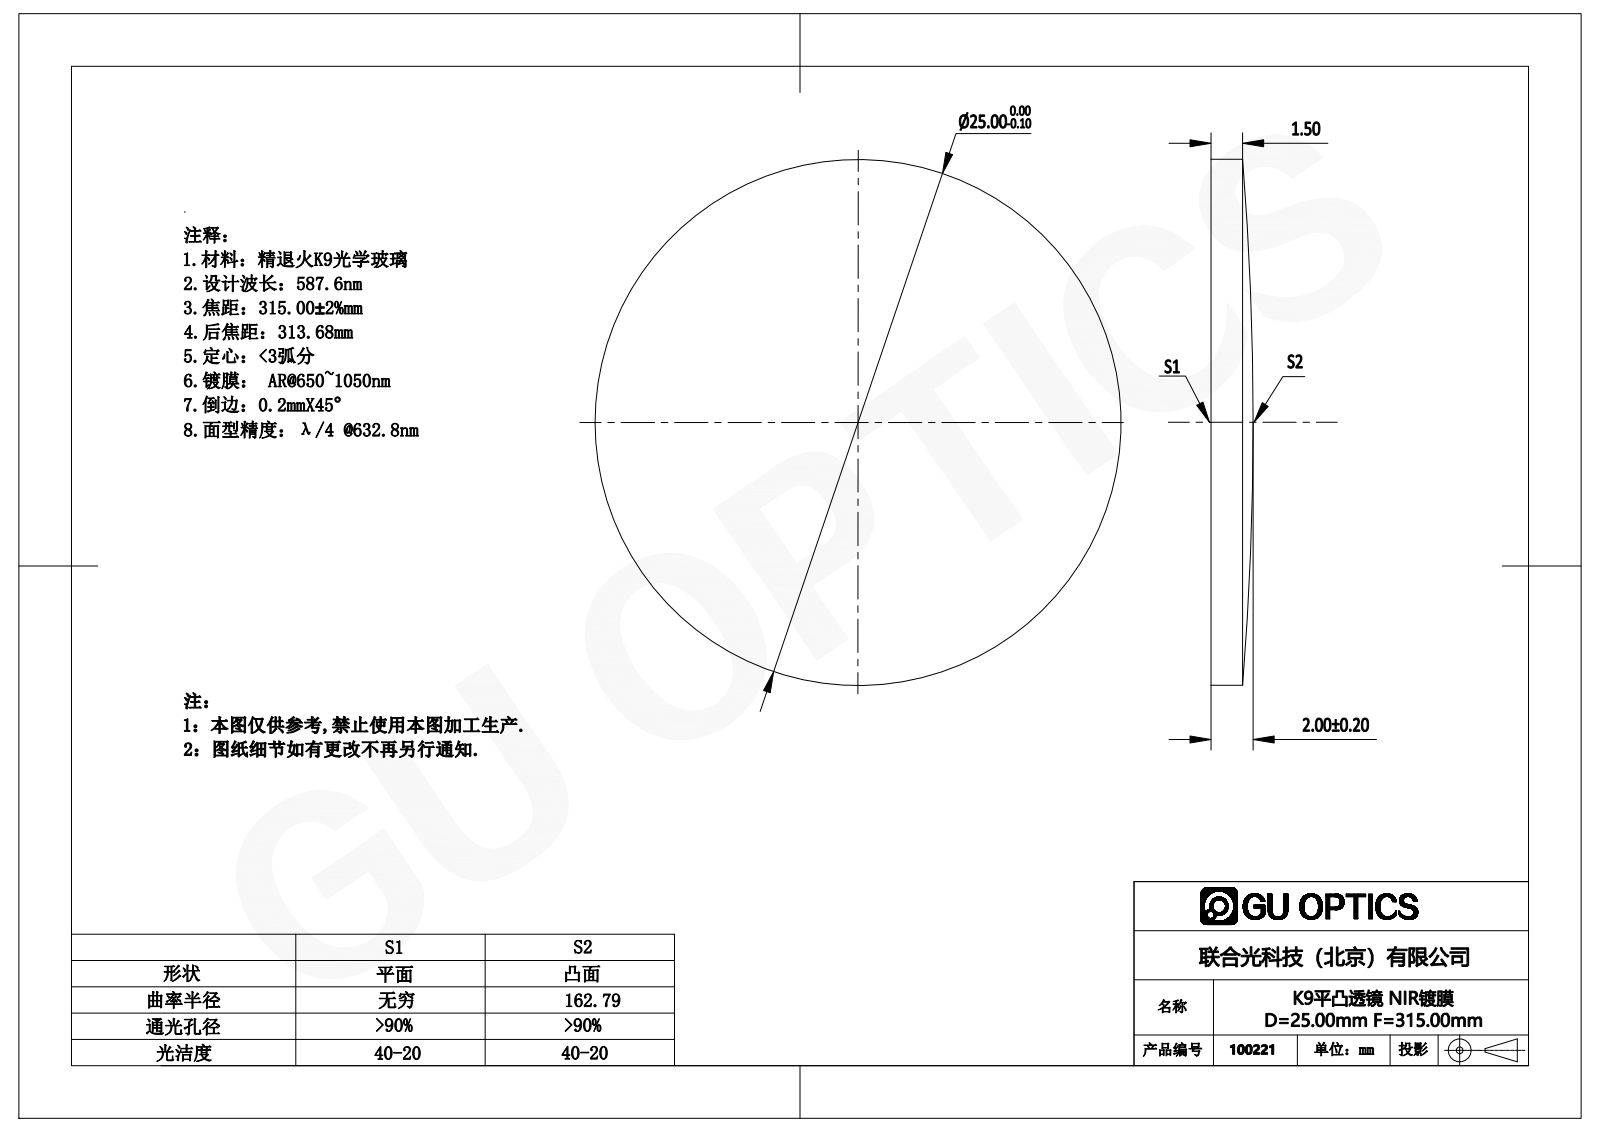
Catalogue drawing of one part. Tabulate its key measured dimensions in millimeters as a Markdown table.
| quantity | value |
| --- | --- |
| part name | 100221 |
| STEP written by | SolidWorks 2016 (AUTOMOTIVE_DESIGN) |
| units | millimeters |
| bodies | 1 solid, 5 faces (1 planar, 2 cylindrical, 2 other) |
| overall size | 25 × 25 × 2 |
| volume | 859 mm³ |
| surface area | 1 100 mm² |
| round bosses / shafts (diameter × count) | 25 × 1 |
